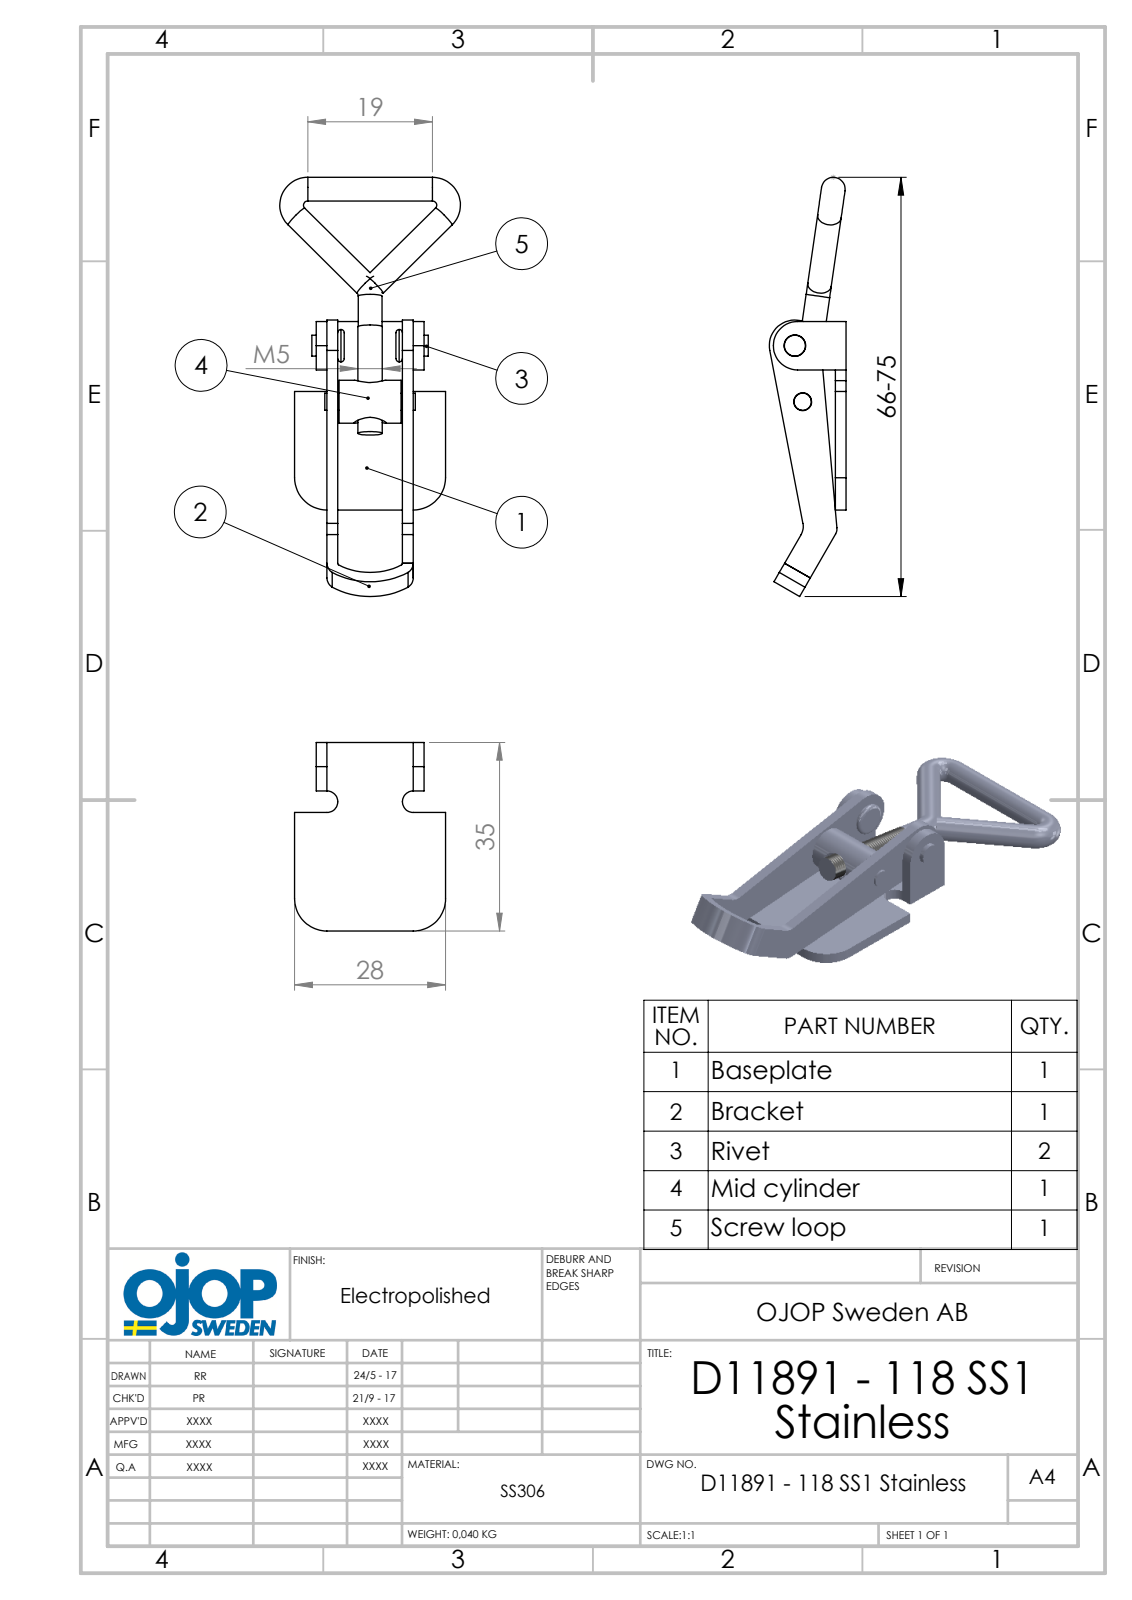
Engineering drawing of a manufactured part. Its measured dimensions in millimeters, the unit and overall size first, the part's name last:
Units: millimetres
Overall size (bounding box): 77.83 × 33.52 × 14.25
Round holes (diameter × count): ⌀3.3 ×1, ⌀4 ×1, ⌀4.6 ×1
Round bosses / shafts (diameter × count): ⌀4.4 ×4, ⌀8 ×1, ⌀4.5 ×1, ⌀3.9 ×1, ⌀3.2 ×1
Partial cylindrical surfaces — rounded edges, fillets, slot ends (radius × count): R2 ×3, R0.5 ×2, R2.5 ×2, R6 ×2, R3 ×1, R4.5 ×1, R4.75 ×1, R11.39 ×1
Main face-to-face distances: 2, 14, 16, 12, 4, 18, 20, 22, 6, 4.25
Hole centre spacings: 10.51
Volume: 5 721 mm³ · Surface area: 6 677 mm²
Bodies: 7 solids, 117 faces (41 planar, 56 cylindrical, 20 other)
Part name (STEP PRODUCT): platta; bygel; nit; rulle (+2 more)
STEP written by: SolidWorks 2015 (AUTOMOTIVE_DESIGN)
